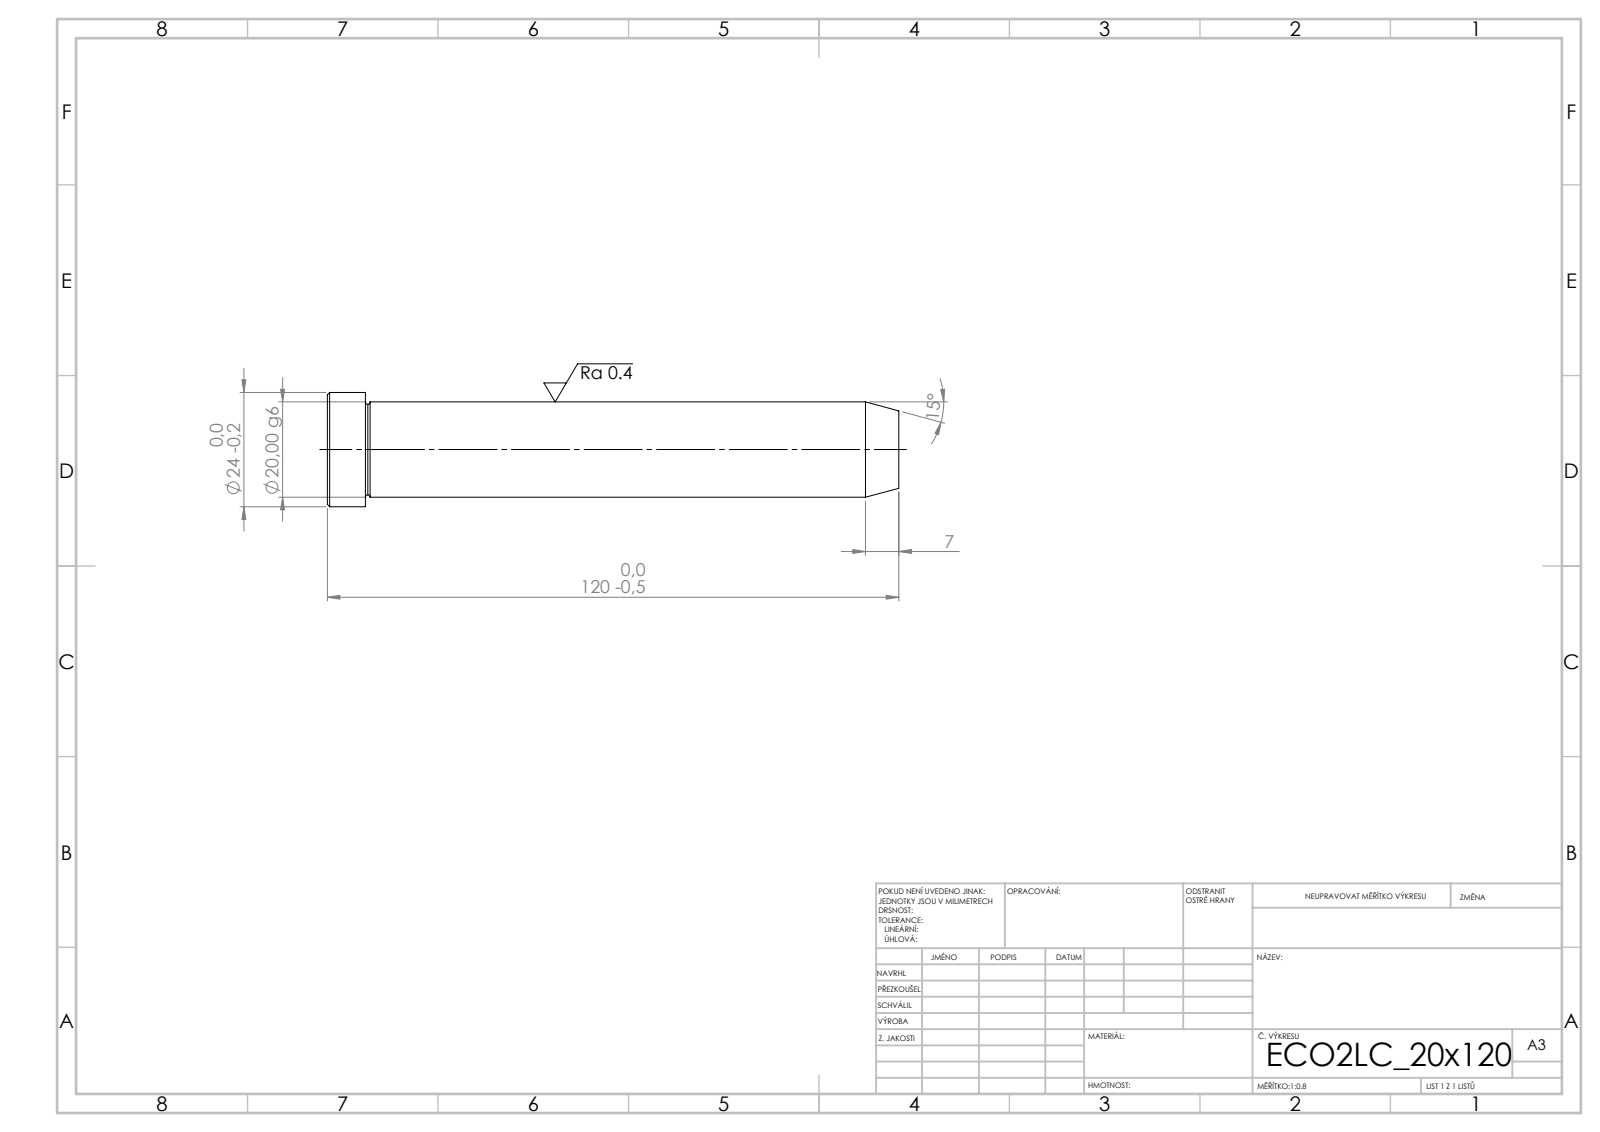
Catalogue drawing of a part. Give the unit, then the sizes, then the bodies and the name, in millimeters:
Units: millimetres
Overall size (bounding box): 120 × 24 × 24
Round bosses / shafts (diameter × count): ⌀24 ×1, ⌀20 ×1
Main face-to-face distances: 120, 112, 8
Volume: 38 385 mm³ · Surface area: 8 421 mm²
Bodies: 1 solid, 15 faces (3 planar, 4 cylindrical, 8 other)
STEP written by: SolidWorks 2019 (CONFIG_CONTROL_DESIGN)
